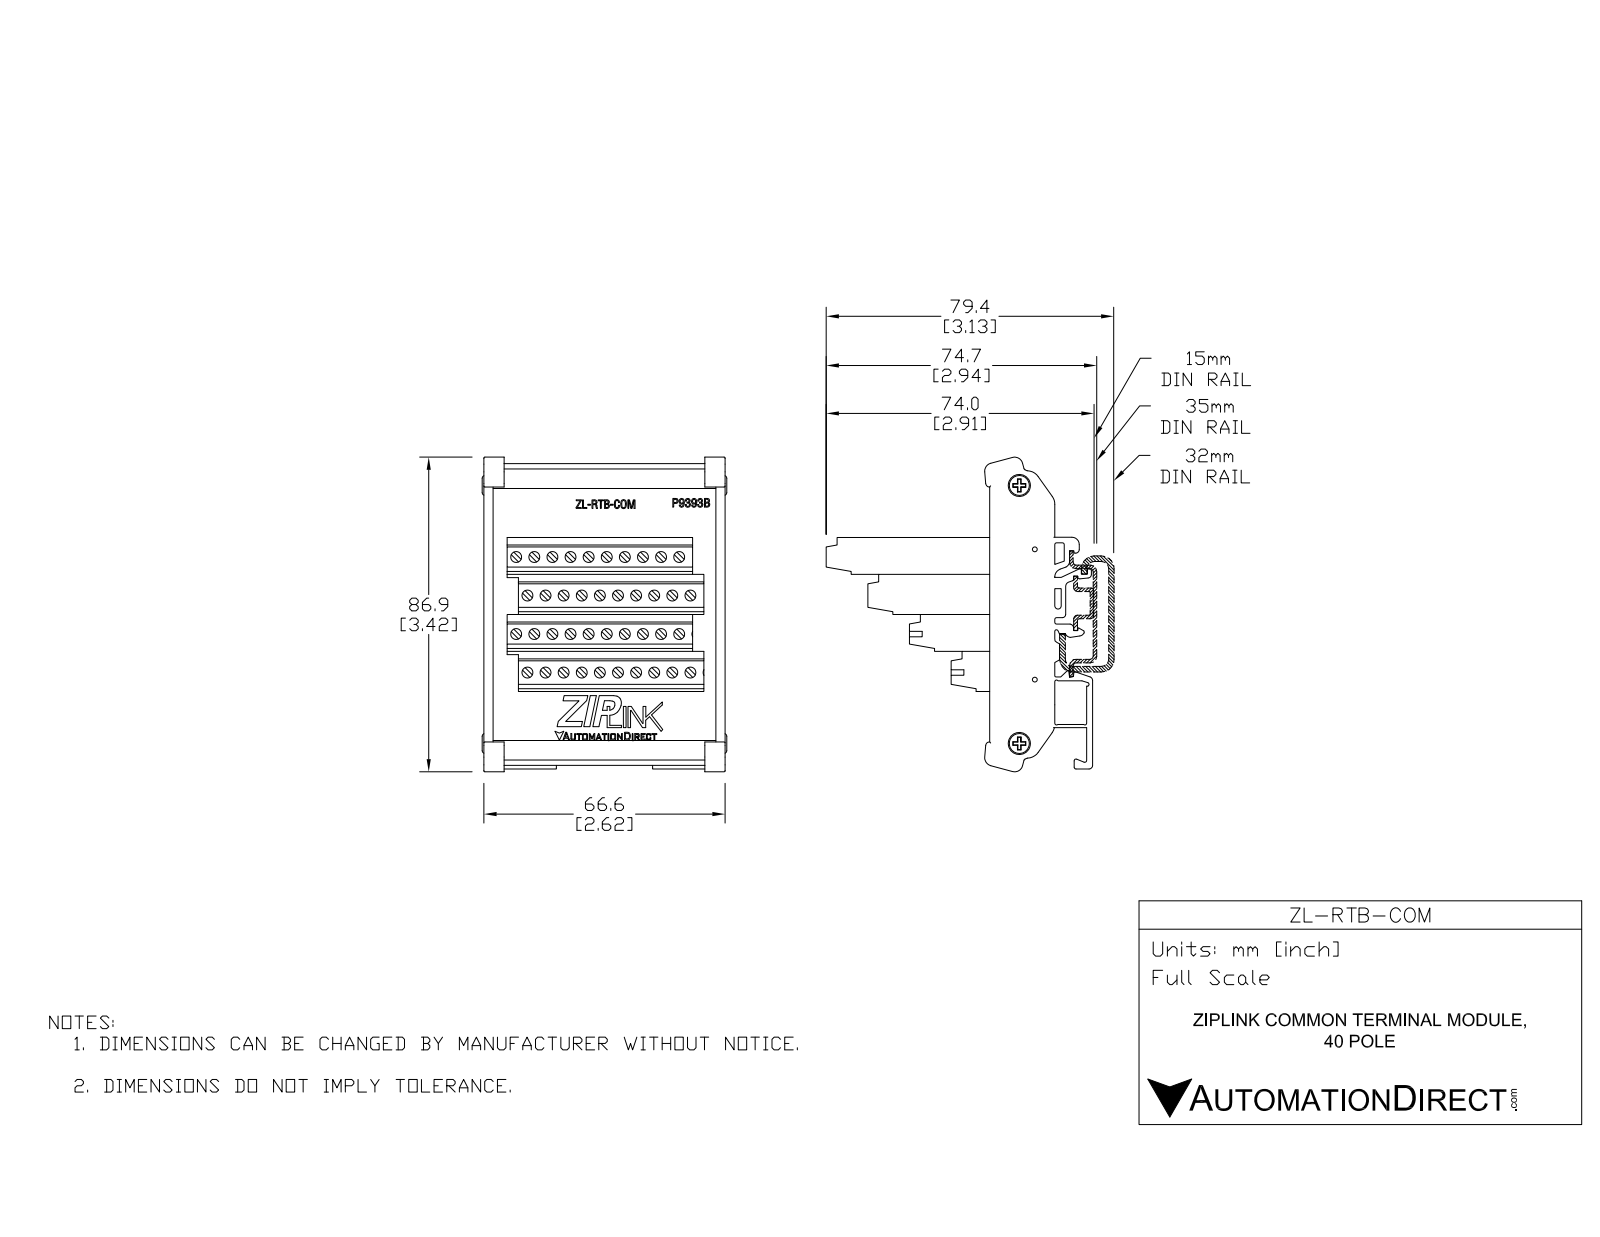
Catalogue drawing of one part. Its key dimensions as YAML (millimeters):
part_name: "ZL-RTB-COM"
step_written_by: "SolidWorks 2016 (AUTOMOTIVE_DESIGN)"
units: millimeters
bodies: {solids: 10, faces: 2339, planar: 1608, cylindrical: 606, other: 125}
overall_size: [86.83, 73.54, 67.5]
volume: 104816
surface_area: 72497
round_holes:
  - {diameter: 1.27, count: 40}
  - {diameter: 3, count: 40}
  - {diameter: 1.33, count: 2}
  - {diameter: 3.5, count: 2}
  - {diameter: 6.1, count: 2}
round_bosses_or_shafts:
  - {diameter: 5.5, count: 2}
  - {diameter: 4, count: 2}
  - {diameter: 3, count: 2}
partial_cylinders:
  - {radius: 0.5, count: 50}
  - {radius: 0.51, count: 50}
  - {radius: 0.25, count: 24}
  - {radius: 0.3, count: 10}
  - {radius: 0.9, count: 5}
  - {radius: 0.98, count: 5}
  - {radius: 1.26, count: 5}
  - {radius: 2, count: 4}
face_to_face_distances: [1.5, 5.41, 1.55, 11.5, 4.54, 6.09, 6.91, 11.45, 13, 6.04]
hole_center_spacings: [10.46, 5, 12.63, 10, 16.11, 15, 20.24, 20]
